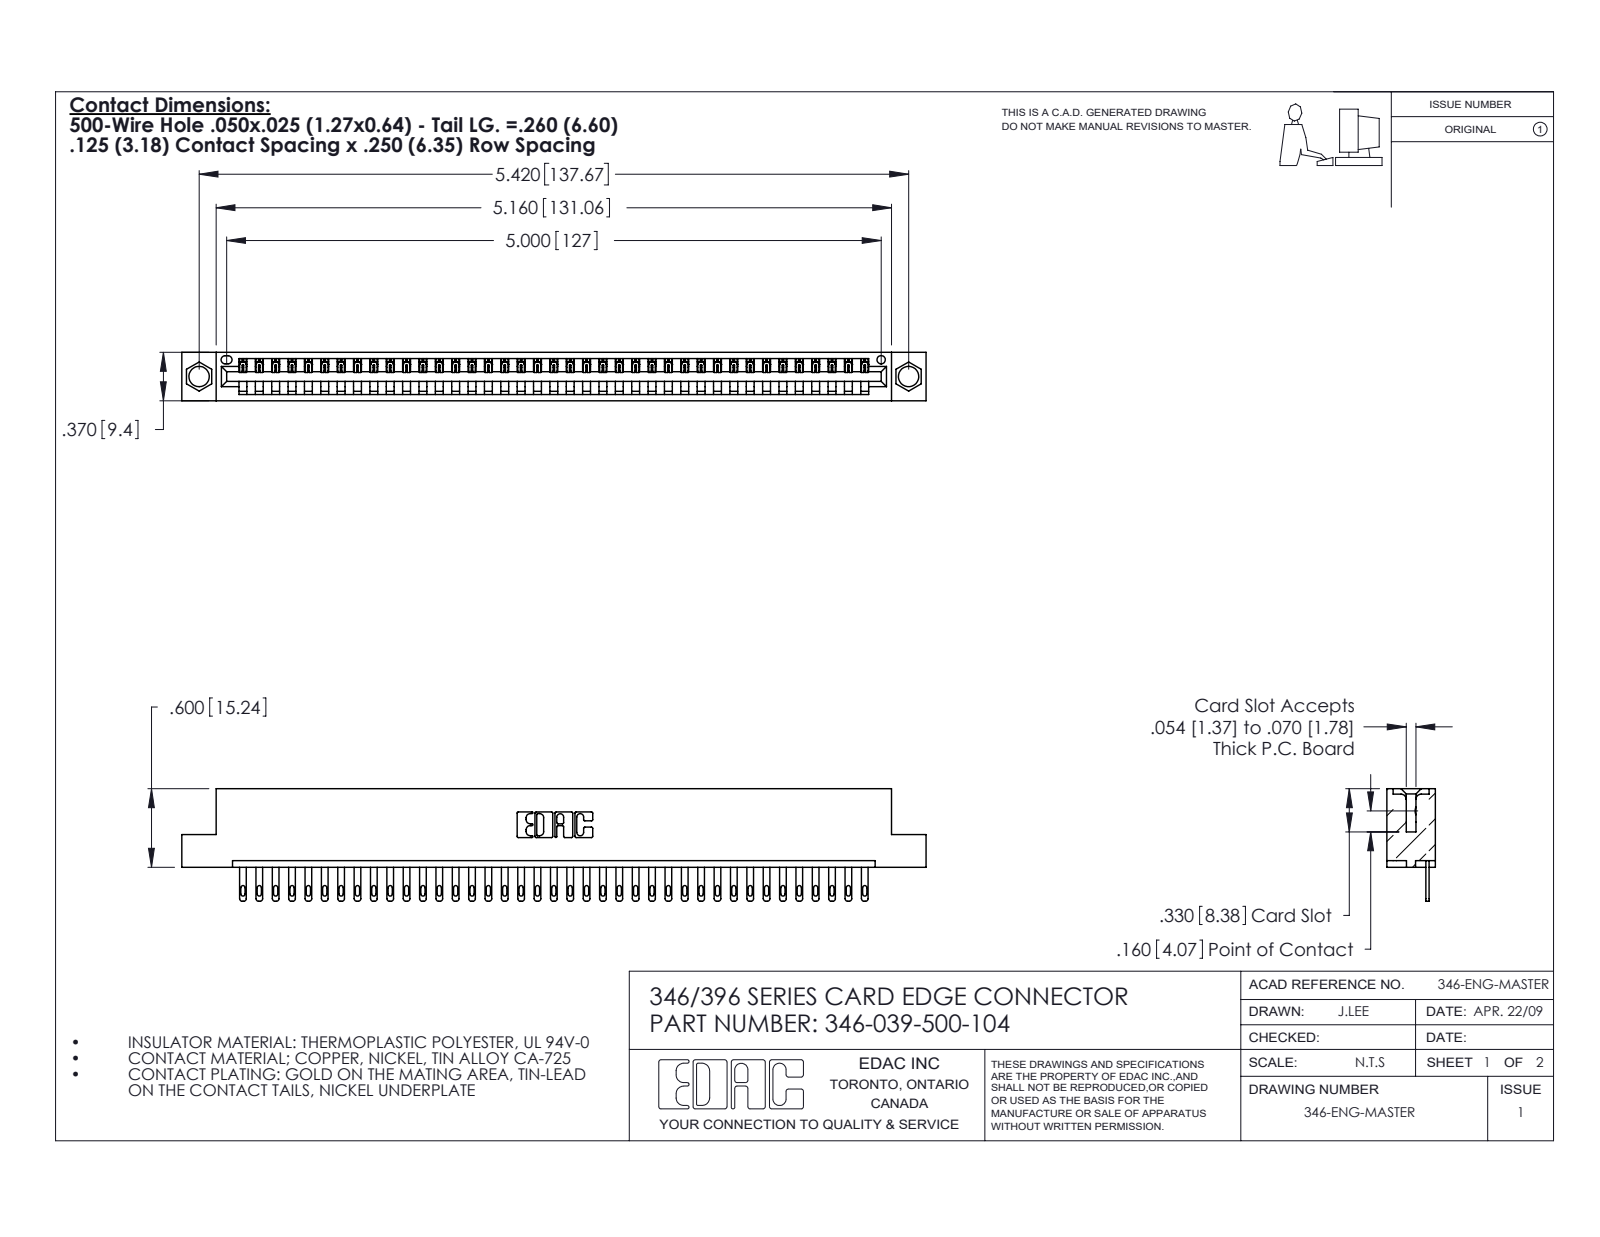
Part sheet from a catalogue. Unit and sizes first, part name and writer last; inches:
Units: inches
Overall size (bounding box): 5.685 × 0.86 × 0.37
Round holes (diameter × count): ⌀0.156 ×2, ⌀0.064 ×1
Partial cylindrical surfaces — rounded edges, fillets, slot ends (radius × count): R0.006 ×78, R0.016 ×78, R0.02 ×78, R0.01 ×22, R0.007 ×6, R0.031 ×6, R0.026 ×3, R0.031 ×2
Main face-to-face distances: 0.048, 0.322, 0.37, 0.25, 0.072, 0.298, 0.025, 0.148, 0.222, 0.1
Hole centre spacings: 0.246, 5.211, 5.42
Volume: 0.837 in³ · Surface area: 26.42 in²
Bodies: 40 solids, 2242 faces (1416 planar, 826 cylindrical, 0 other)
Part name (STEP PRODUCT): 345-292-001_345-293-100; 346-039-500-104; 346 Part_Flush Mounting Lugs - 0.156 Dia-TH
STEP written by: SolidWorks 2020 (CONFIG_CONTROL_DESIGN)
